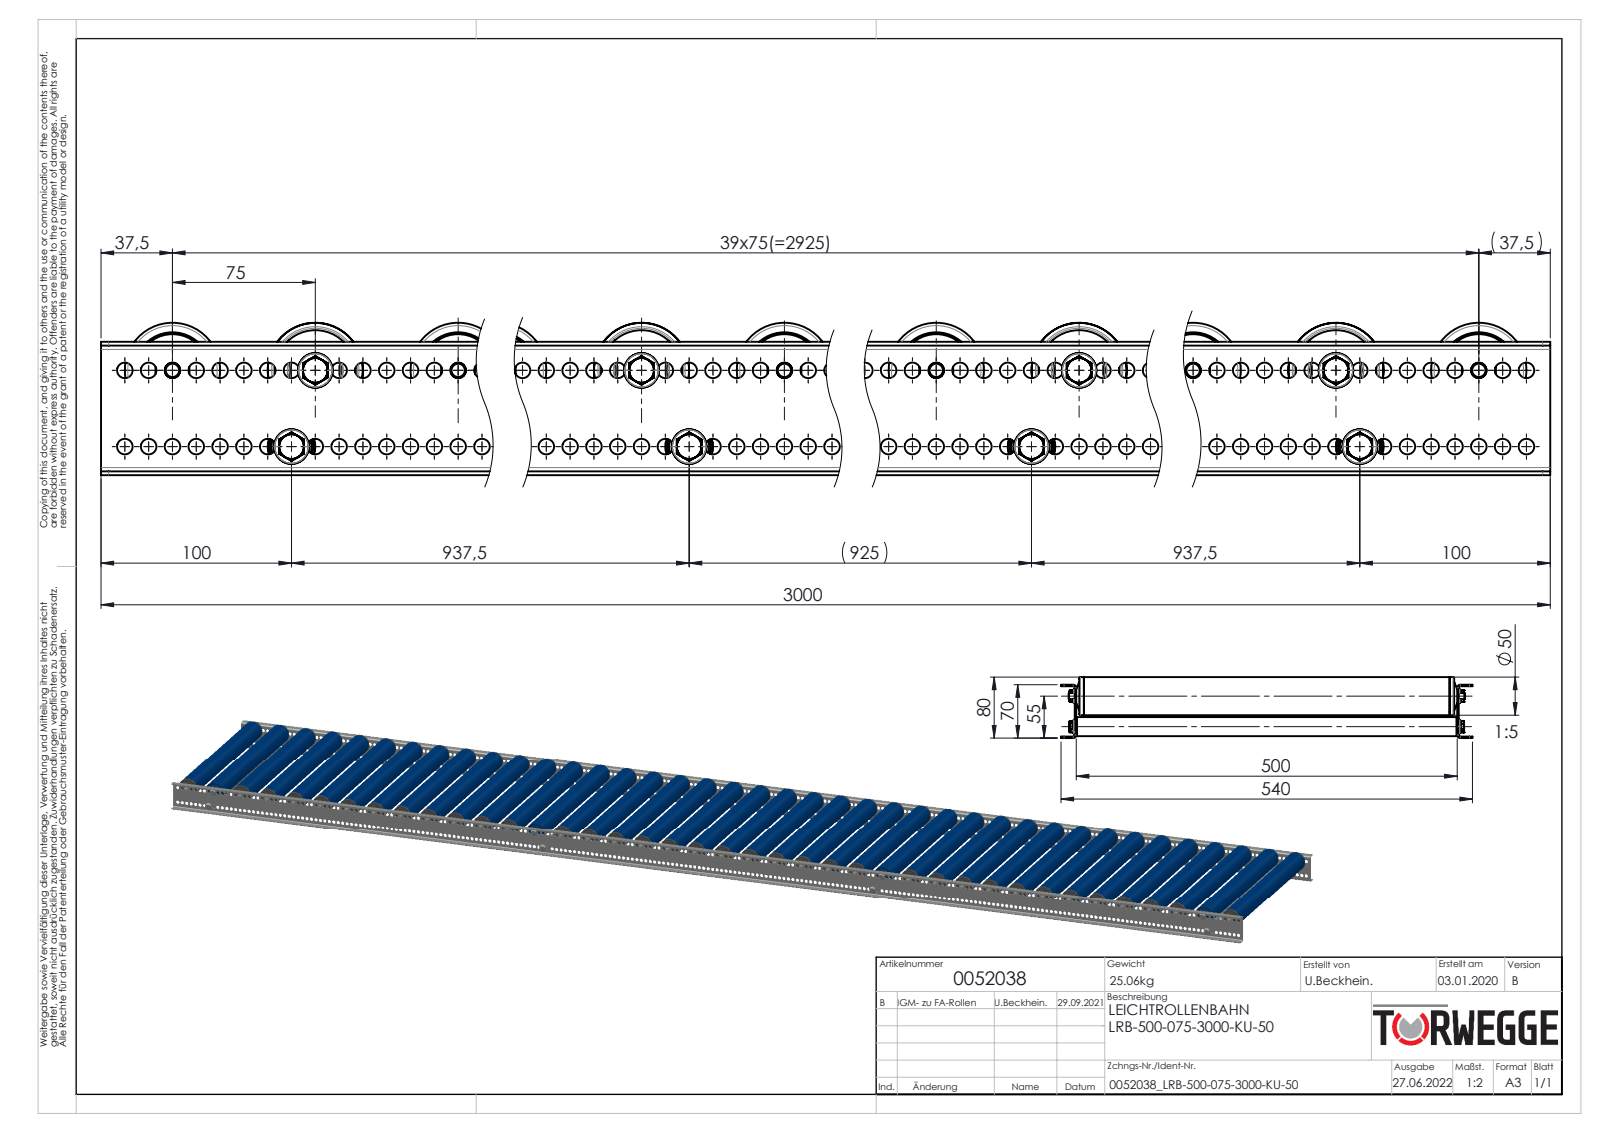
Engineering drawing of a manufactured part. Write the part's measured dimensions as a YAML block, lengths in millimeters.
part_name: "Profil_LRB-20x70x20x2_KFG_S109080_U-PROFIL-20-70-20-2-LRB-L=3000; 0026267_Typ-KUT100-50x2,8-8_Lageboden-schematisch; 0039780-Achse-ST-Ø12-KFG_IGM8-AL=500; 0024178_Passscheibe_DIN988_12x18x1 (+8 more)"
step_written_by: "SolidWorks 2020 (AUTOMOTIVE_DESIGN)"
units: millimeters
bodies: {solids: 634, faces: 12220, planar: 3052, cylindrical: 5720, other: 3448}
overall_size: [3000, 540, 80]
volume: 12800000
surface_area: 9467000
round_holes:
  - {diameter: 8.2, count: 478}
  - {diameter: 7.6, count: 36}
  - {diameter: 8, count: 36}
  - {diameter: 25, count: 36}
  - {diameter: 30, count: 36}
  - {diameter: 35, count: 36}
  - {diameter: 39.4, count: 36}
  - {diameter: 40, count: 36}
  - {diameter: 6.8, count: 8}
  - {diameter: 12, count: 4}
  - {diameter: 12.1, count: 4}
  - {diameter: 16, count: 4}
round_bosses_or_shafts:
  - {diameter: 50, count: 40}
  - {diameter: 44.4, count: 36}
  - {diameter: 38, count: 36}
  - {diameter: 36, count: 36}
  - {diameter: 33, count: 36}
  - {diameter: 22, count: 36}
  - {diameter: 21, count: 36}
  - {diameter: 25, count: 8}
partial_cylinders:
  - {radius: 0.6, count: 72}
  - {radius: 0.75, count: 72}
  - {radius: 2.45, count: 72}
  - {radius: 4.87, count: 36}
  - {radius: 7, count: 36}
  - {radius: 4, count: 8}
  - {radius: 2, count: 4}
  - {radius: 2.5, count: 4}
face_to_face_distances: [2, 502, 68, 500, 504, 70, 66, 492, 12, 6]
hole_center_spacings: [12.5, 25, 37.5, 50, 62.5, 75, 87.5, 100]
